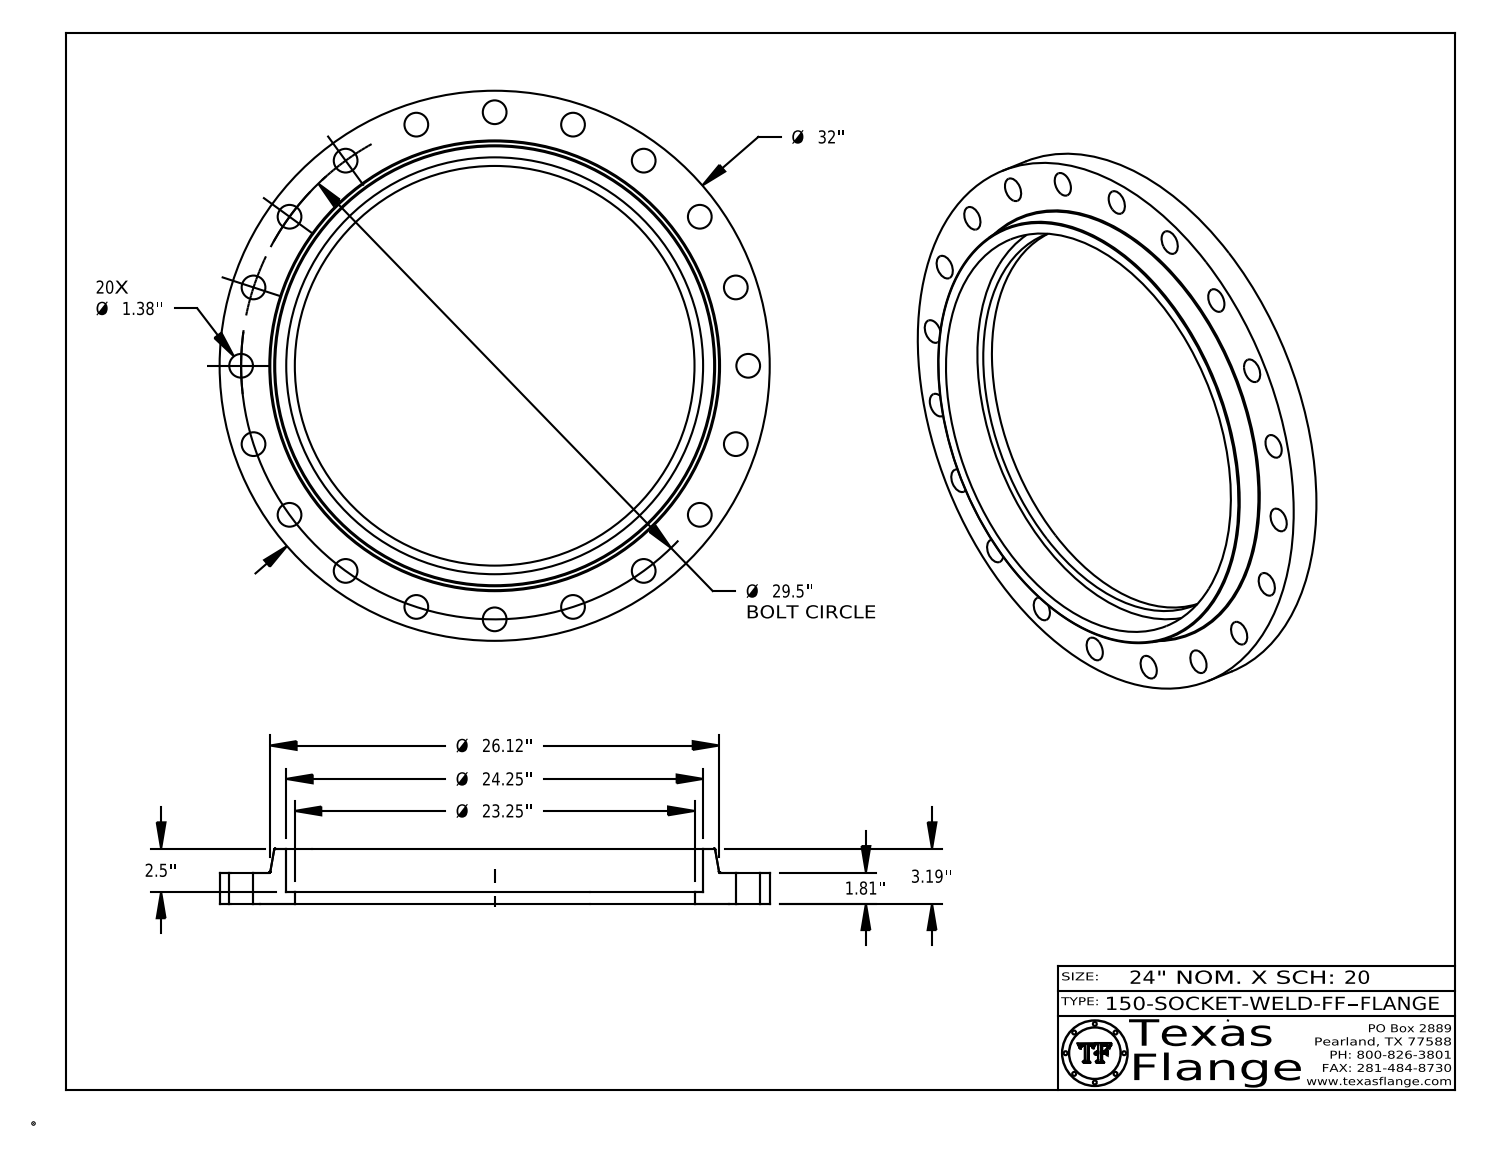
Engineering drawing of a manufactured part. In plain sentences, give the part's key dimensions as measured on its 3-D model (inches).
The part is named "150-SOCKET-WELD-FF". Its 3-D file was written by "CATIA V5 STEP AP214 (AUTOMOTIVE_DESIGN)". It is 1 solid with 442 faces: 370 planar, 66 cylindrical and 6 other. Overall it measures 32 by 32 by 3.19 inches. Its volume is 679.7 cubic inches and its surface area 1 371 square inches. Round holes: 20 of diameter 1.38, 1 of diameter 0.495, 1 of diameter 23.25, 1 of diameter 24.25. Round bosses or shafts: 8 of diameter 0.03, 1 of diameter 32, 1 of diameter 0.39. The main face-to-face distances are 1.81, 3.19, 1.38, 0.69, 1.12, 2.5, 1.795, 1.105, 0.015, 1.395. The hole center spacings are 14.75, 29.137, 4.615, 17.34, 20.859, 23.866, 26.285, 9.116.
